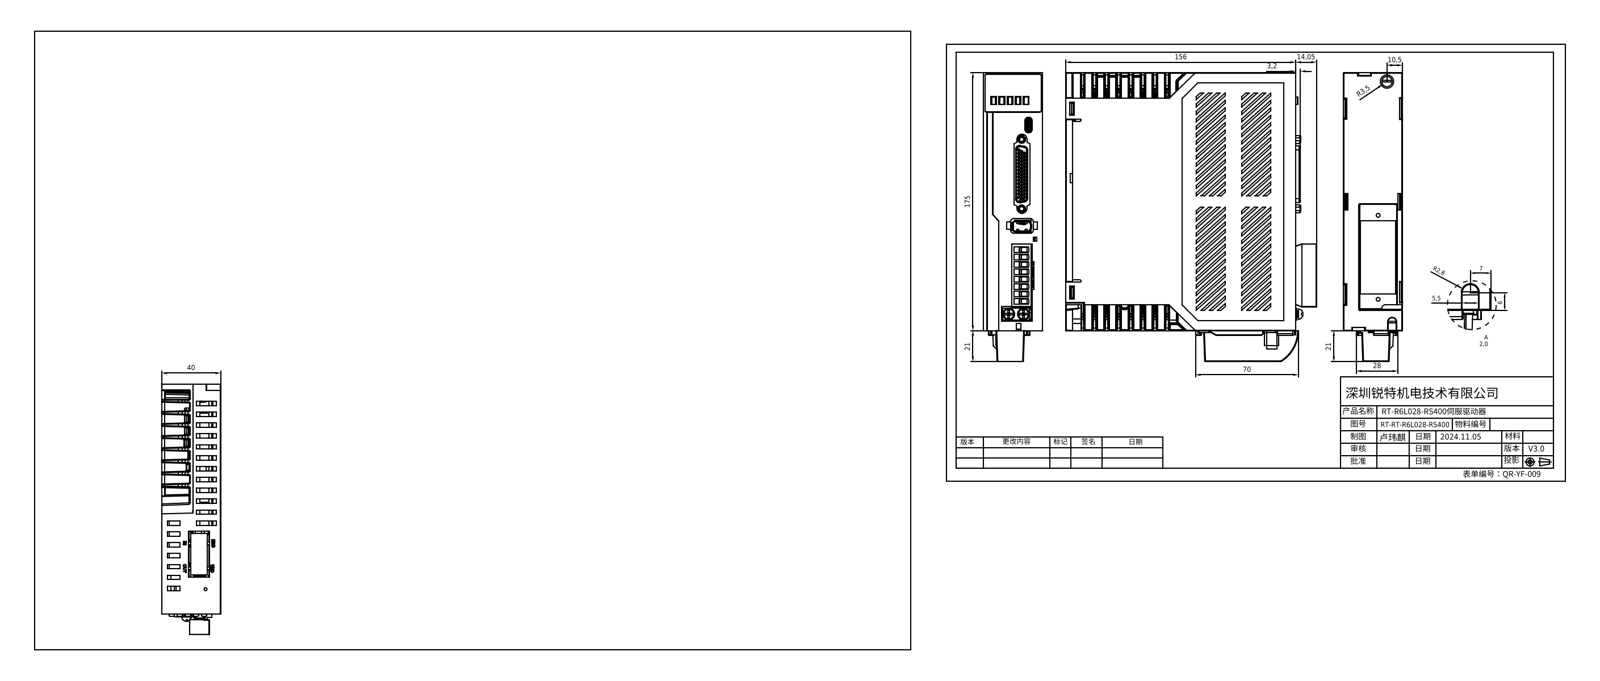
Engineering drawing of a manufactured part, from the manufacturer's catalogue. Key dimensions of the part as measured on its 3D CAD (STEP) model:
Part name (STEP PRODUCT): RT-R6L028
STEP written by: CREO PARAMETRIC BY PTC INC, 2021063 (CONFIG_CONTROL_DESIGN)
Units: millimetres
Bodies: 3 solids, 6446 faces (4413 planar, 1271 cylindrical, 762 other)
Overall size (bounding box): 196 × 170.04 × 40
Volume: 274 567 mm³ · Surface area: 320 490 mm²
Round holes (diameter × count): ⌀2.5 ×6, ⌀1.2 ×2, ⌀2.6 ×2, ⌀35 ×2, ⌀2 ×1, ⌀7 ×1, ⌀10 ×1
Round bosses / shafts (diameter × count): ⌀0.73 ×44, ⌀3.5 ×4, ⌀8 ×2, ⌀6 ×2, ⌀4 ×2, ⌀3.2 ×2, ⌀2.84 ×2, ⌀2.8 ×2
Partial cylindrical surfaces — rounded edges, fillets, slot ends (radius × count): R0.5 ×322, R1 ×87, R0.3 ×67, R0.2 ×42, R0.15 ×35, R2 ×34, R0.1 ×26, R0.4 ×22
Main face-to-face distances: 2, 32, 8.2, 4, 16.4, 1.8, 37.8, 6, 24.6, 36
Hole centre spacings: 5.5, 11, 16.5, 6.5, 6.9, 9.96, 10.73, 12
